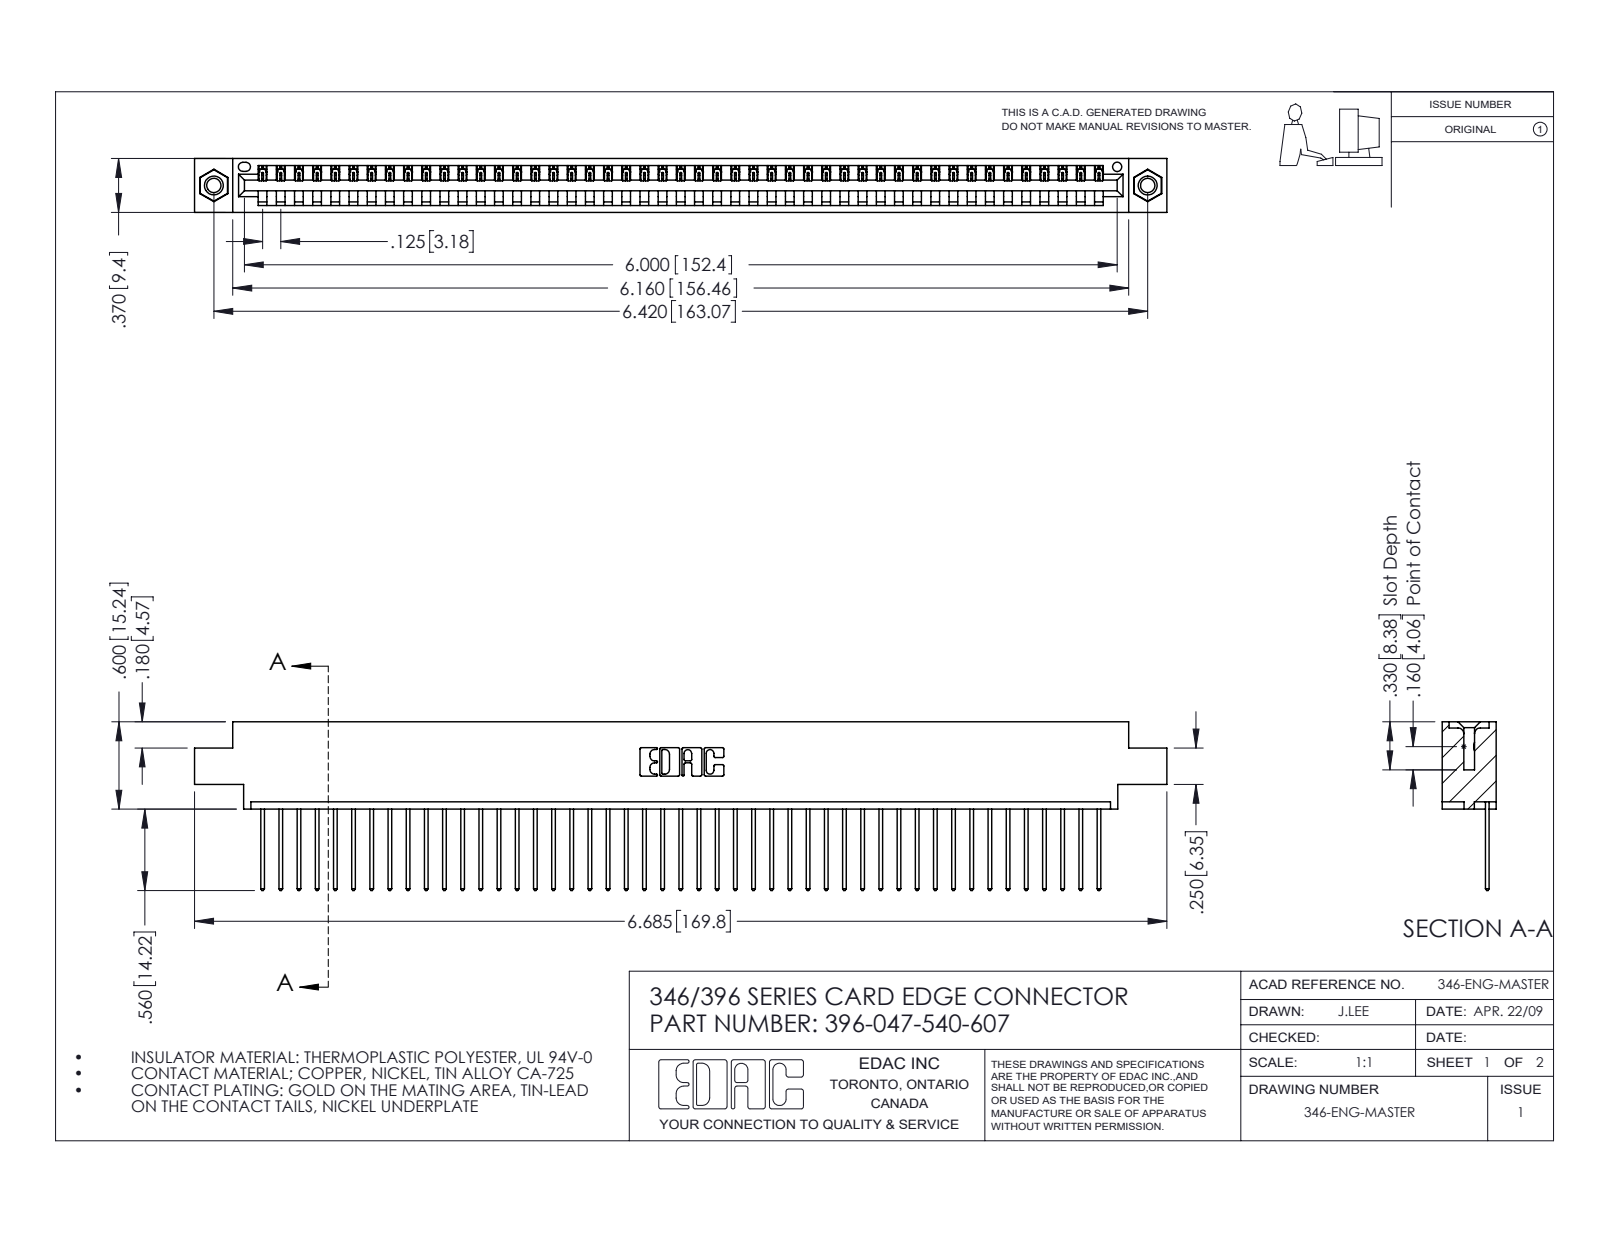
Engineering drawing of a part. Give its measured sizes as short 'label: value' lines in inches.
name: 346 Part_0.170 Offset - 0.156 Dia-TI; 396-047-540-607; 345-250-001_345-250-005-103; 345-292-001_345-293-140
written by: SolidWorks 2016 (CONFIG_CONTROL_DESIGN)
unit: in
bodies: 50 solids, 2912 faces (1992 planar, 904 cylindrical, 16 other)
size: 6.685 × 1.16 × 0.37
volume: 0.988 in³; area: 32.46 in²
holes: 2× ⌀0.098, 2× ⌀0.125, 2× ⌀0.156, 1× ⌀0.064
bosses: 2× ⌀0.155
rounds: 94× R0.006, 94× R0.01, 22× R0.01, 6× R0.007, 6× R0.031, 3× R0.026, 2× R0.031, 2× R0.04
face distances: 0.048, 0.322, 0.37, 0.25, 0.072, 0.298, 0.025, 0.222, 0.148, 0.1
hole spacings: 0.246, 6.211, 6.42
